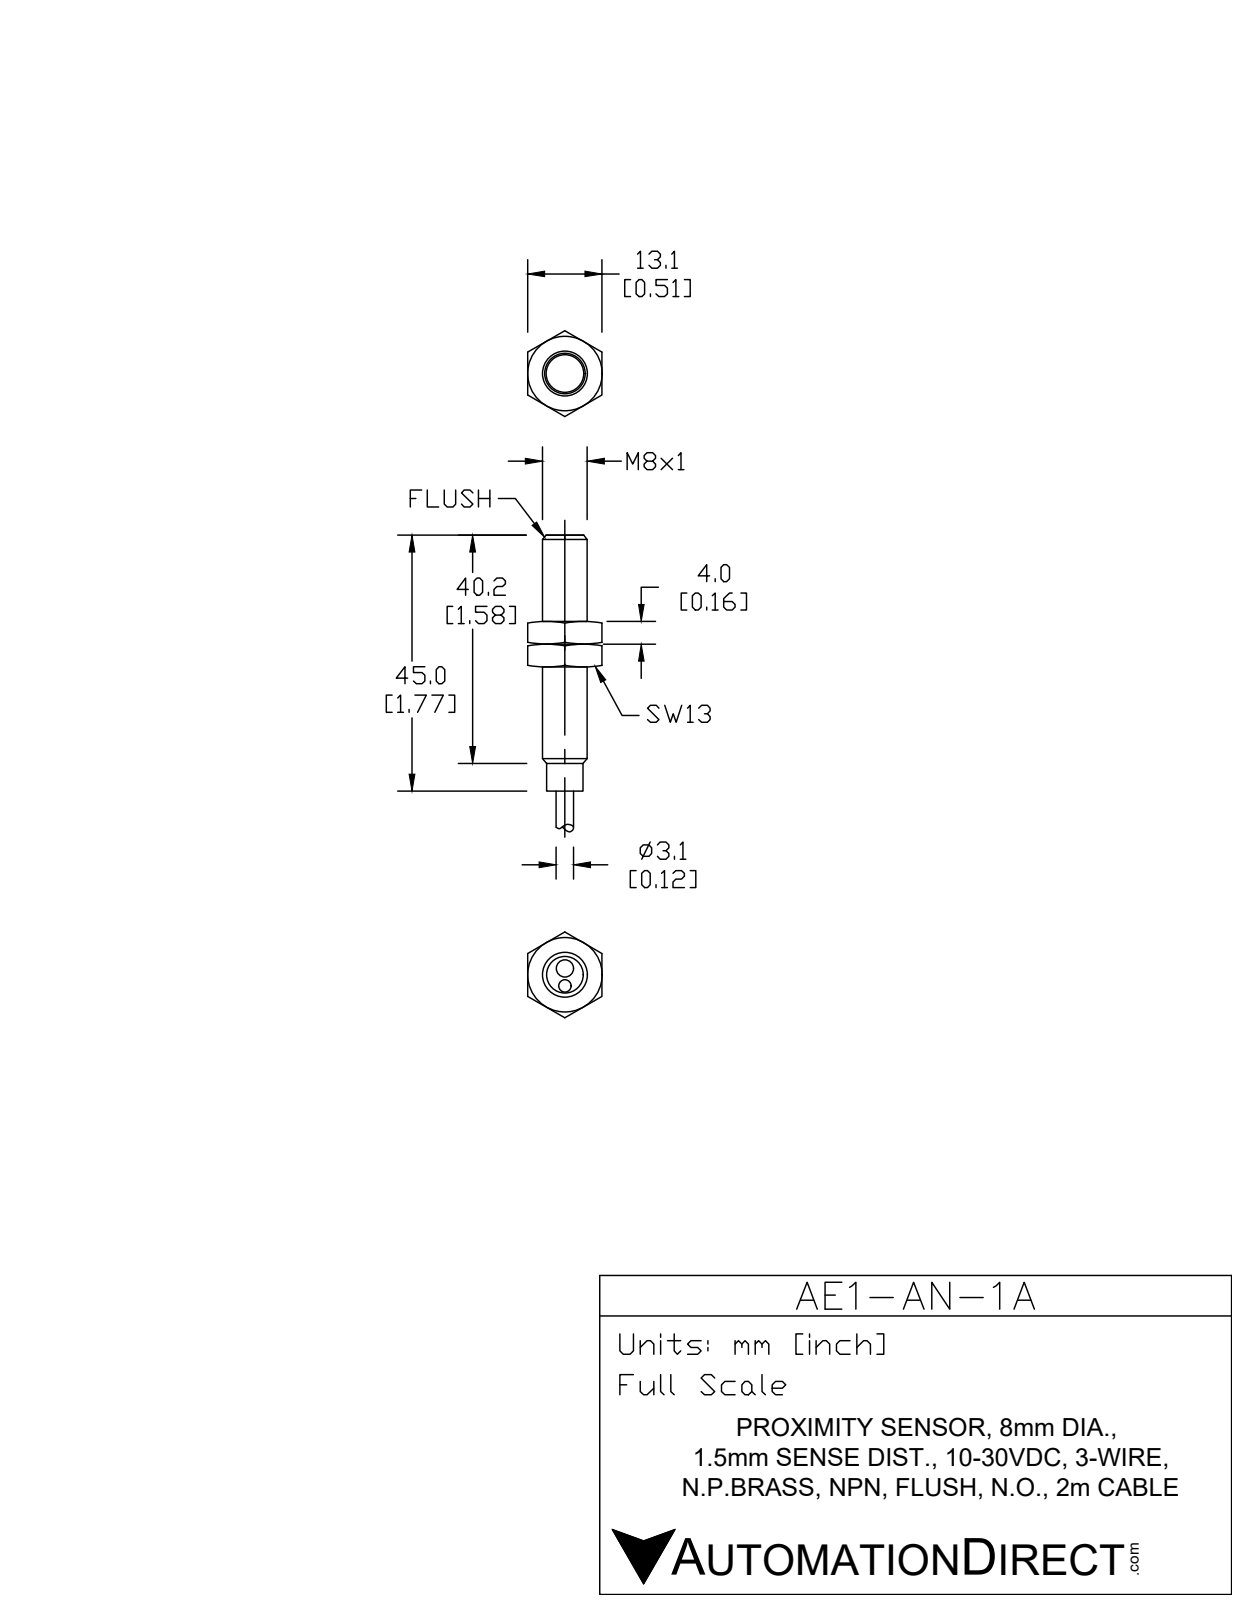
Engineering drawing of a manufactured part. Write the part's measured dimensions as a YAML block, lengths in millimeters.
part_name: "AE1-AN-1A"
step_written_by: "SolidWorks 2017 (AUTOMOTIVE_DESIGN)"
units: millimeters
bodies: {solids: 4, faces: 30, planar: 10, cylindrical: 12, other: 8}
overall_size: [82.6, 8, 8]
volume: 2430
surface_area: 1745
round_holes:
  - {diameter: 3.1, count: 1}
  - {diameter: 5.8, count: 1}
round_bosses_or_shafts:
  - {diameter: 8, count: 1}
  - {diameter: 6.5, count: 1}
  - {diameter: 6.5, count: 1}
face_to_face_distances: [39.9, 40.2, 44.5, 44.2, 4.3, 2.4, 42.6, 42.3, 1.9, 82.6]
hole_center_spacings: [1.1]
